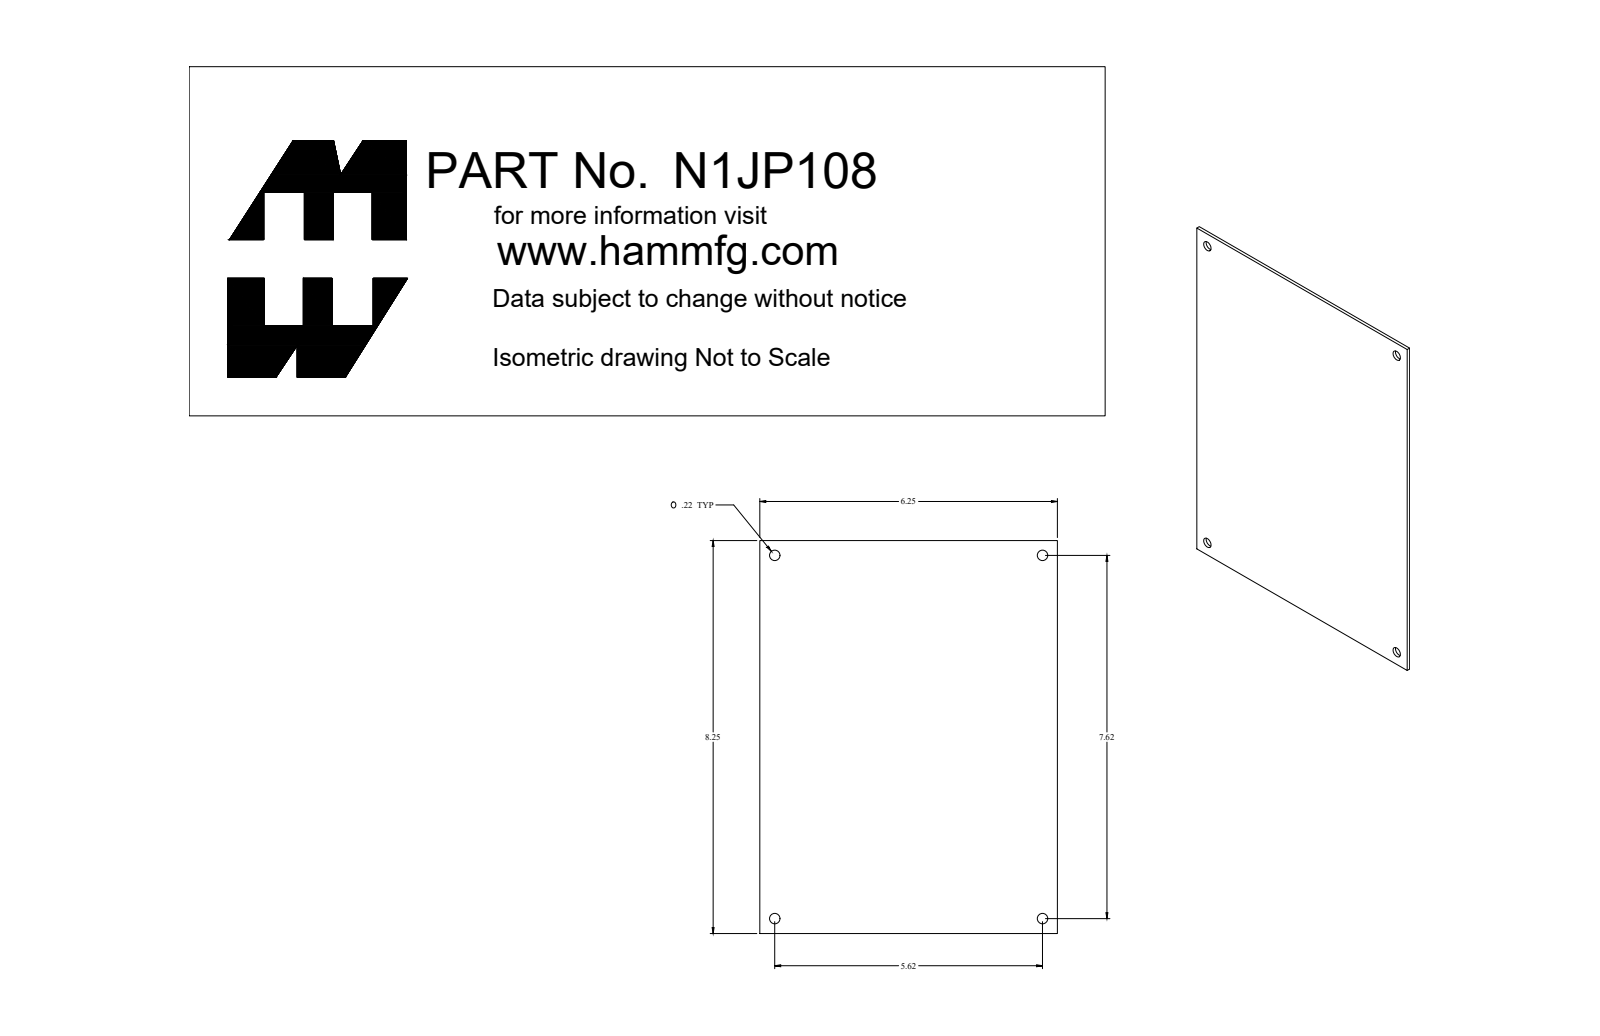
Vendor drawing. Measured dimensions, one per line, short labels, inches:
name: N1JP108
written by: SolidWorks 2018 (AUTOMOTIVE_DESIGN)
unit: in
bodies: 1 solid, 18 faces (6 planar, 12 cylindrical, 0 other)
size: 8.25 × 6.25 × 0.072
volume: 3.696 in³; area: 105 in²
holes: 4× ⌀0.265
rounds: 4× R0.125
face distances: 0.072, 6.25, 8.25
hole spacings: 5.625, 7.625, 9.475
